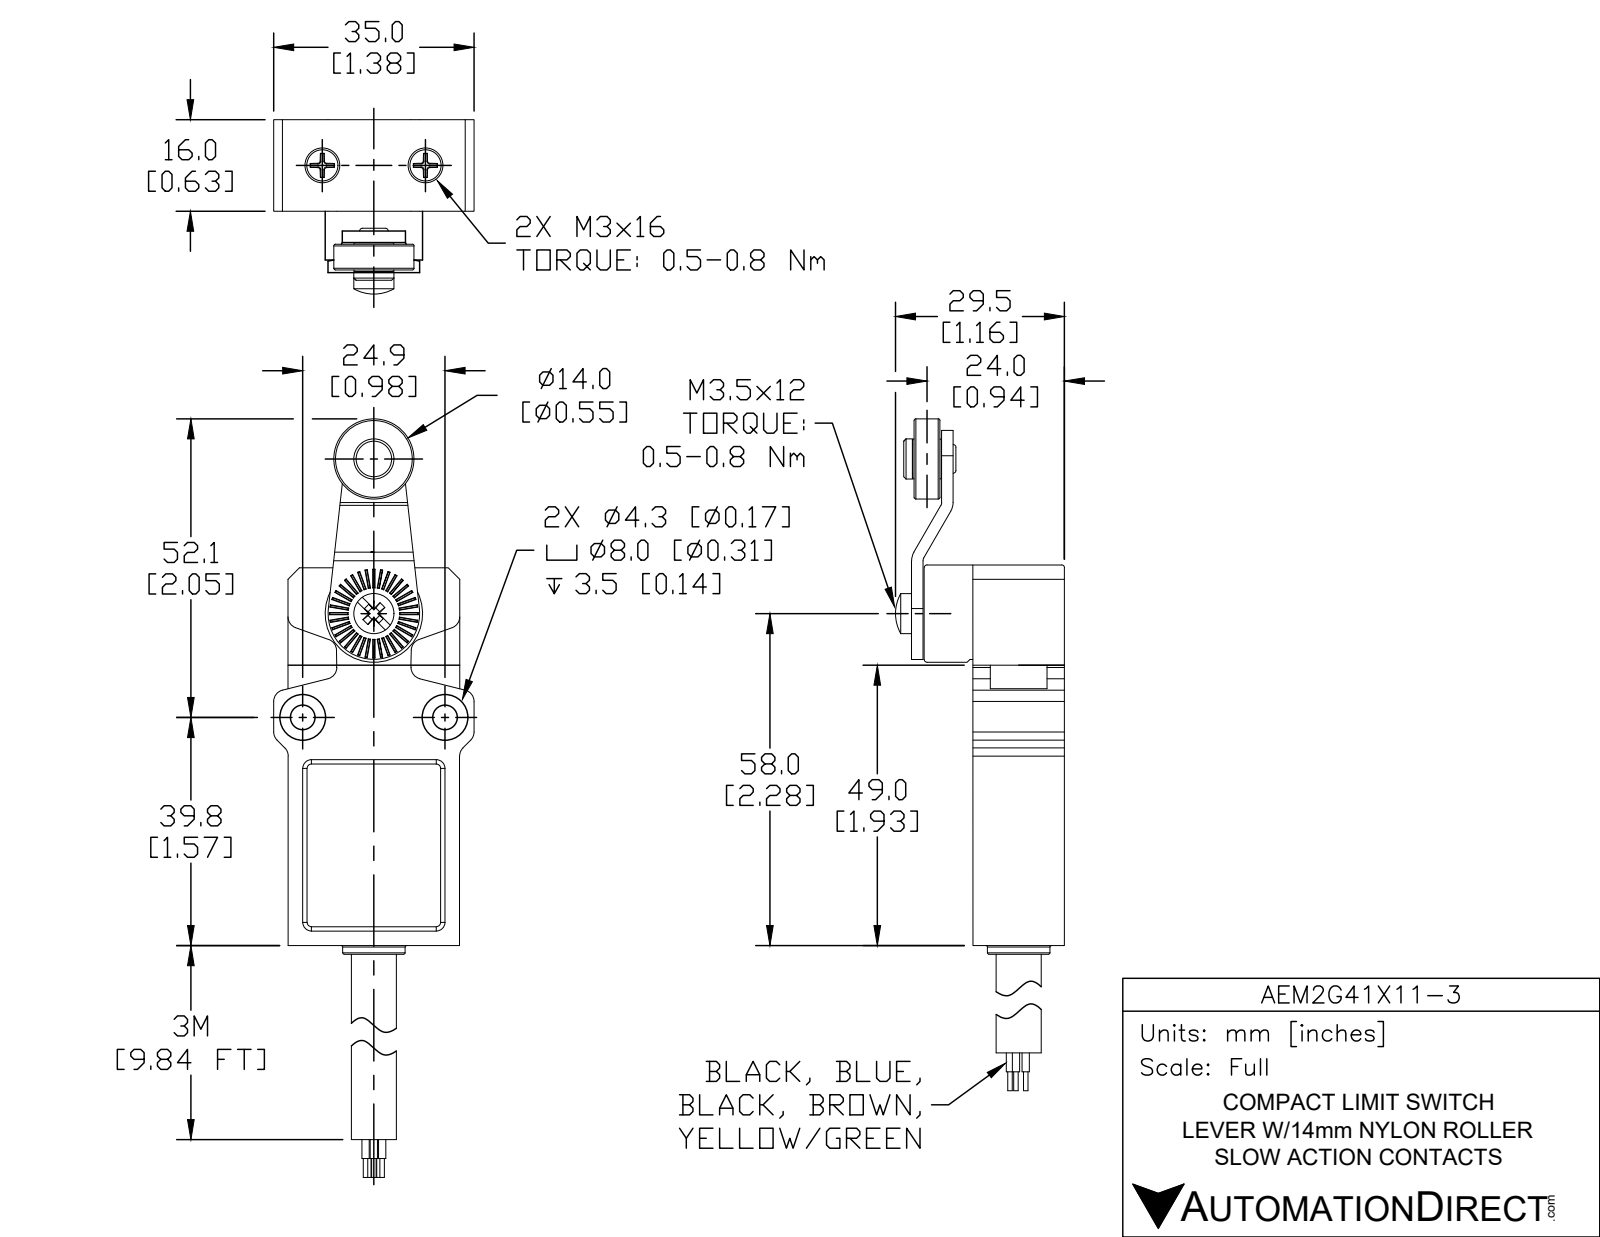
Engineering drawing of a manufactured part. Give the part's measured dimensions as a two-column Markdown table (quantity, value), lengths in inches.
| quantity | value |
| --- | --- |
| part name | AEM2G41X11-3_Default |
| STEP written by | SolidWorks 2021 (CONFIG_CONTROL_DESIGN) |
| units | inches |
| bodies | 6 solids, 527 faces (294 planar, 68 cylindrical, 165 other) |
| overall size | 4.102 × 1.378 × 1.26 |
| volume | 1.862 in³ |
| surface area | 17.41 in² |
| round holes (diameter × count) | 0.118 × 2, 0.173 × 2, 0.323 × 2, 0.098 × 1, 0.161 × 1, 0.197 × 1, 0.224 × 1 |
| round bosses / shafts (diameter × count) | 0.276 × 2, 0.157 × 2, 0.622 × 1, 0.551 × 1, 0.394 × 1, 0.323 × 1, 0.236 × 1, 0.197 × 1 |
| partial cylindrical surfaces (radius × count) | 0.079 × 8, 0.039 × 2, 0.118 × 2, 0.256 × 1, 0.315 × 1 |
| main face-to-face distances | 0.63, 1.181, 1.929, 0.354, 0.079, 0.984, 0.28, 0.902, 0.102, 0.472 |
| hole center spacings | 0.863, 1.82, 0.748, 0.984, 1.043 |
